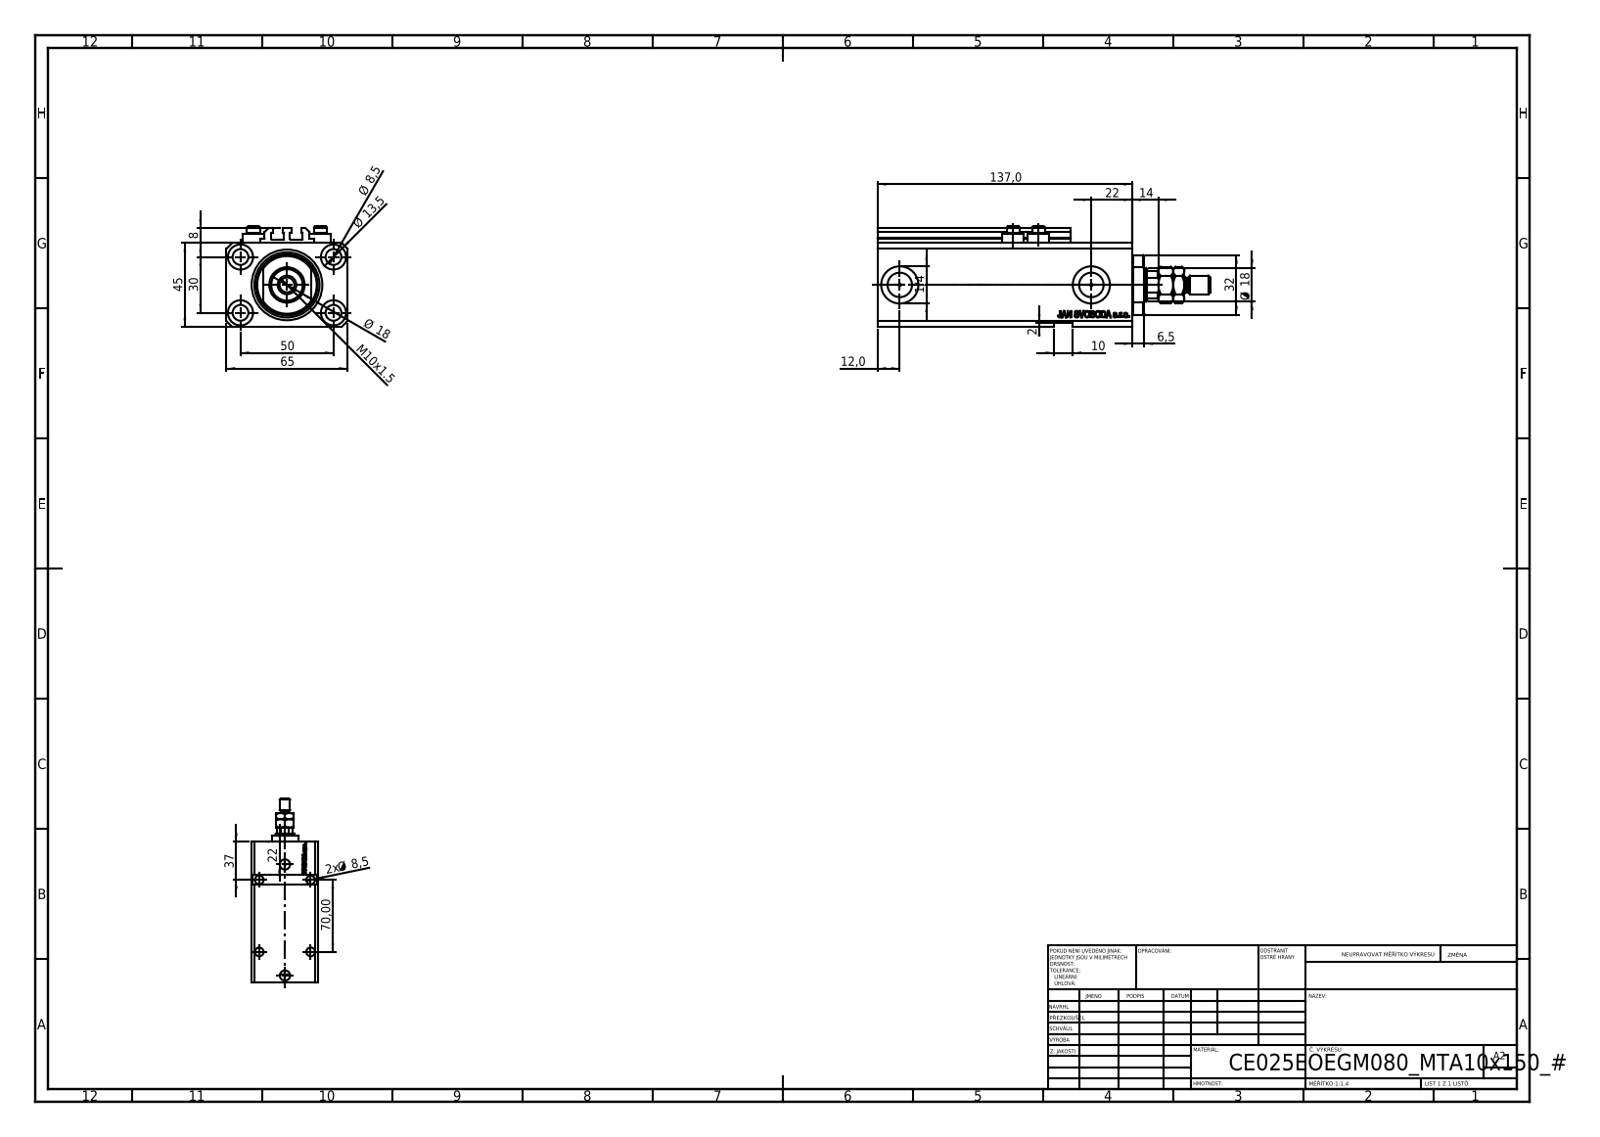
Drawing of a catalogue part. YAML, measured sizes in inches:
part_name: "MTA; V250CE_C_VCP; V250CE_E_Body; ALLEN BOLT V250CE (+1 more)"
step_written_by: "SolidWorks 2019 (CONFIG_CONTROL_DESIGN)"
units: inches
bodies: {solids: 9, faces: 1136, planar: 526, cylindrical: 150, other: 460}
overall_size: [7.047, 2.559, 2.126]
volume: 21.66
surface_area: 147.7
round_holes:
  - {diameter: 0.335, count: 9}
  - {diameter: 0.049, count: 4}
  - {diameter: 0.157, count: 4}
  - {diameter: 0.531, count: 4}
  - {diameter: 0.394, count: 2}
  - {diameter: 0.518, count: 2}
  - {diameter: 0.787, count: 2}
  - {diameter: 0.709, count: 1}
  - {diameter: 0.984, count: 1}
  - {diameter: 1.496, count: 1}
round_bosses_or_shafts:
  - {diameter: 0.457, count: 4}
  - {diameter: 0.276, count: 4}
  - {diameter: 0.394, count: 1}
  - {diameter: 0.315, count: 1}
partial_cylinders:
  - {radius: 0.008, count: 10}
  - {radius: 0.335, count: 1}
  - {radius: 0.63, count: 1}
face_to_face_distances: [1.772, 2.559, 1.85, 0.551, 0.079, 4.843, 0.098, 0.394, 0.807, 0.236]
hole_center_spacings: [1.148, 1.969, 0.535, 0.595, 1.098, 1.181, 1.323, 1.324]
